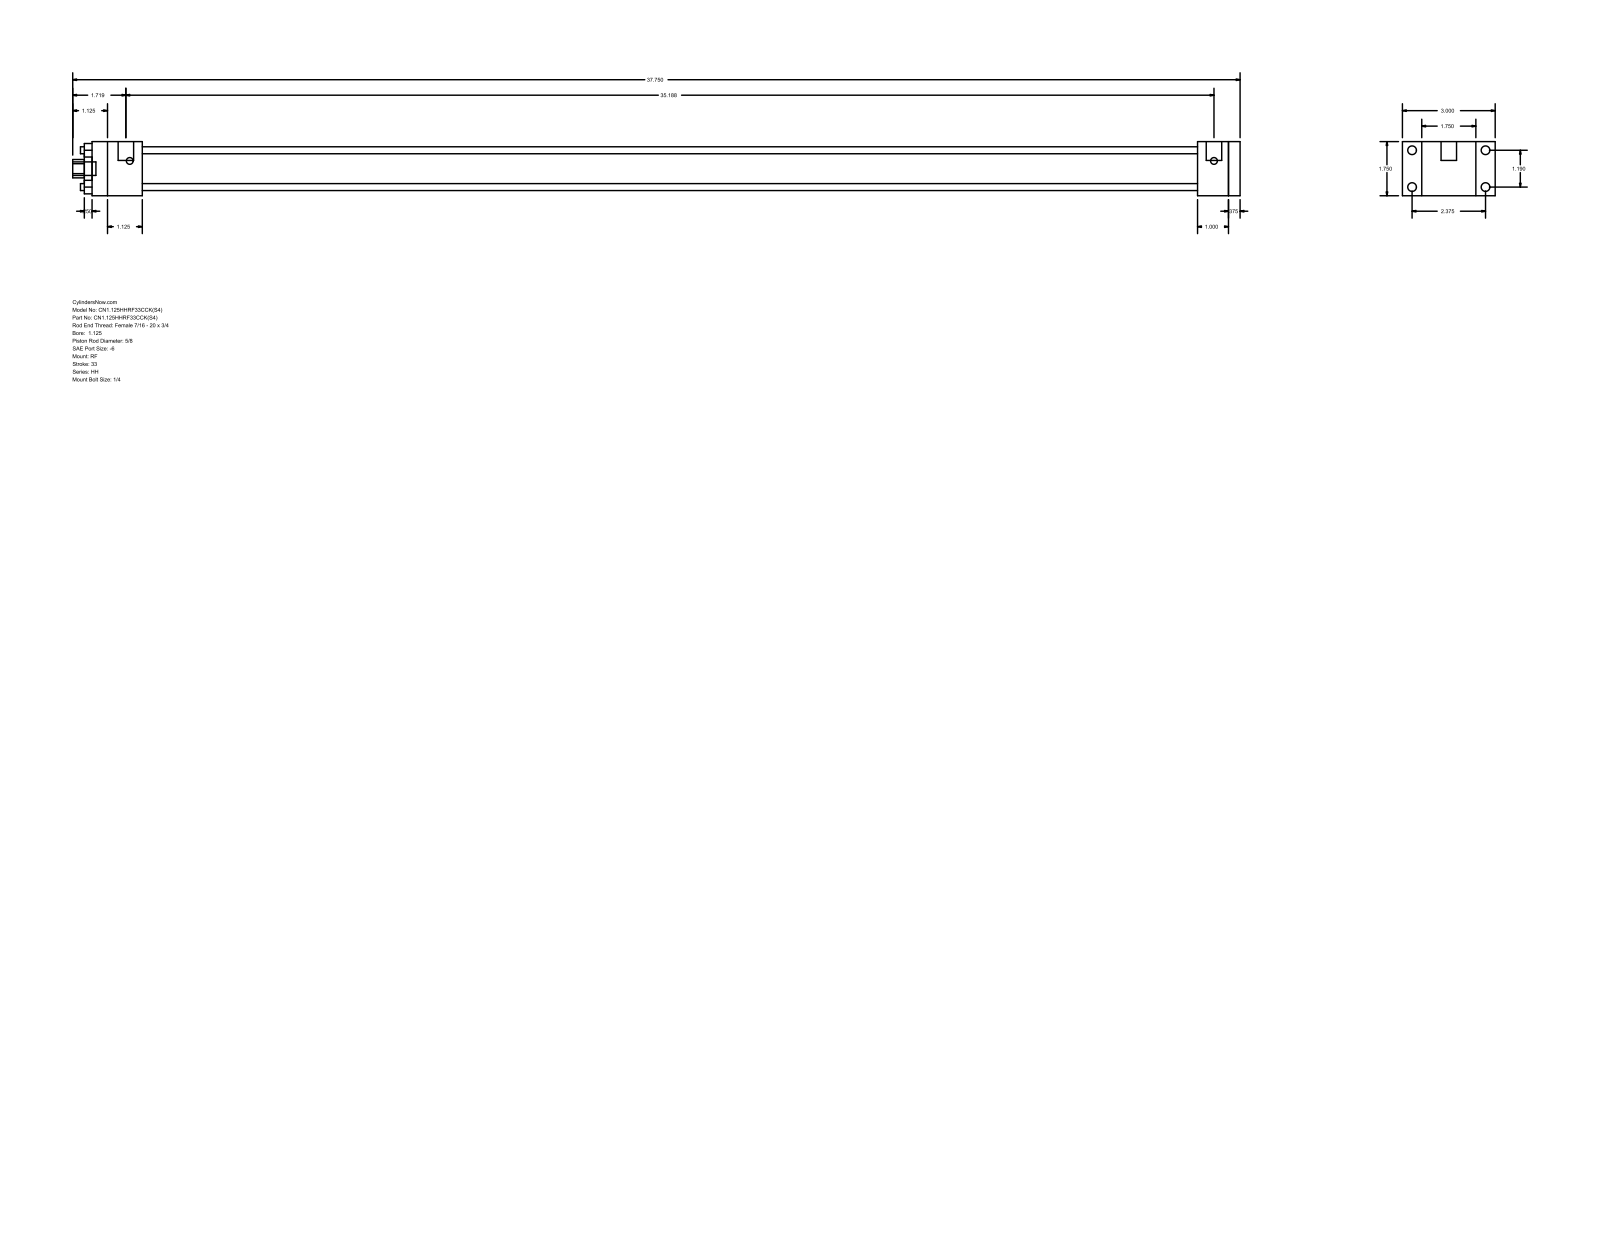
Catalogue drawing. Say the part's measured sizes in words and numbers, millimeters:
The part is named "HH_RF__0112_0.625". Its 3-D file was written by "GSSL Pune (CONFIG_CONTROL_DESIGN)". It is 0 solids with 92 faces: 64 planar, 28 cylindrical and 0 other. Overall it measures 958.85 by 76.2 by 44.45 millimeters. Round holes: 4 of diameter 5.71, 1 of diameter 15.88, 1 of diameter 28.57, 1 of diameter 34.92. Round bosses or shafts: 4 of diameter 7.14, 4 of diameter 5.56, 2 of diameter 12.7, 1 of diameter 11.11. Partial cylindrical surfaces (rounded edges, fillets, slot ends): 1 of radius 7.54. The main face-to-face distances are 44.46, 9.52, 15.87, 892.18, 901.7, 866.77, 25.41, 34.93, 41.27, 908.04. The hole center spacings are 21.37, 30.22, 42.74.
